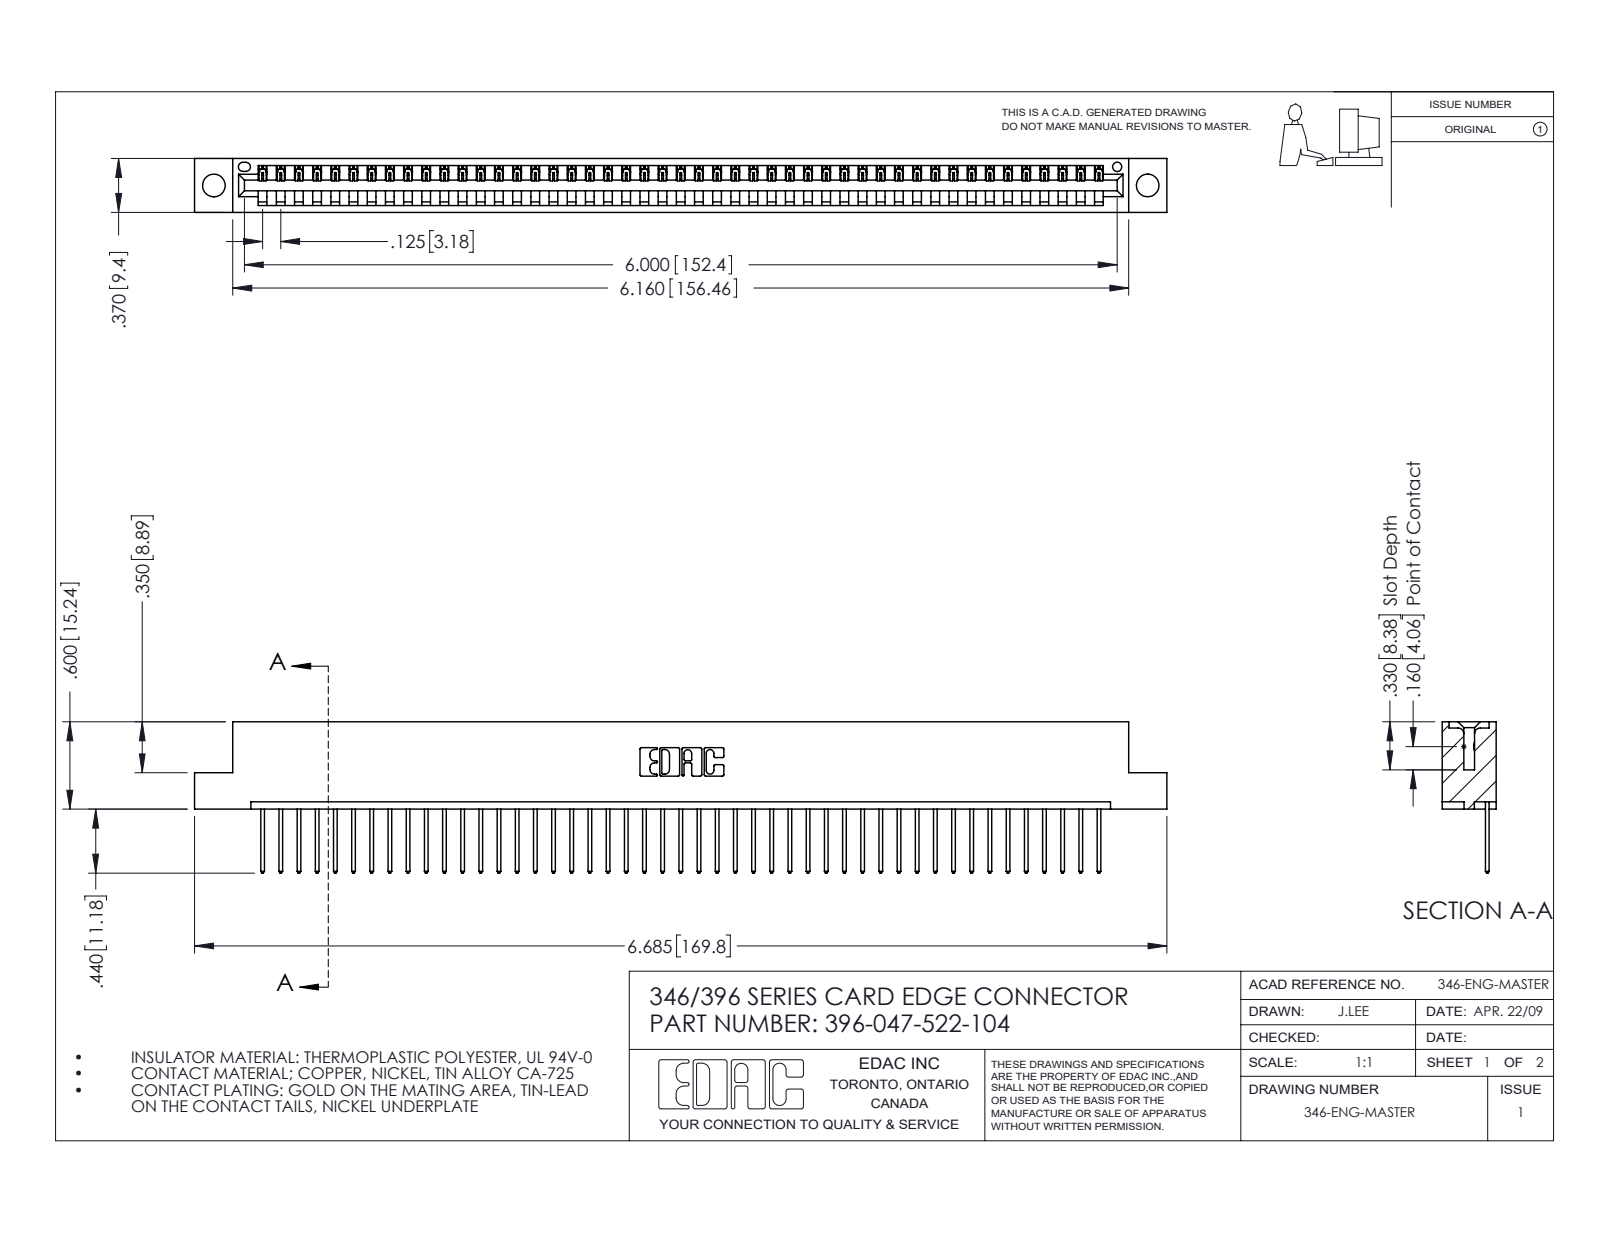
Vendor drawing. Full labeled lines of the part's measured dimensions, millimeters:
Part name (STEP PRODUCT): 345-292-001_345-293-122; 396-047-522-104; 346 Part_Flush Mounting Lugs - 0.156 Dia-TH
STEP written by: SolidWorks 2016 (CONFIG_CONTROL_DESIGN)
Units: millimetres
Bodies: 48 solids, 2848 faces (1956 planar, 892 cylindrical, 0 other)
Overall size (bounding box): 169.8 × 26.4 × 9.4
Volume: 16 200 mm³ · Surface area: 20 290 mm²
Round holes (diameter × count): ⌀4 ×2, ⌀1.6 ×1
Partial cylindrical surfaces — rounded edges, fillets, slot ends (radius × count): R0.2 ×94, R0.3 ×94, R0.3 ×22, R0.2 ×6, R0.8 ×6, R0.7 ×3, R0.8 ×2, R1 ×2
Main face-to-face distances: 1.2, 8.2, 9.4, 6.4, 1.8, 7.6, 0.6, 3.8, 5.6, 2.5
Hole centre spacings: 6.2, 157.8, 163.1
